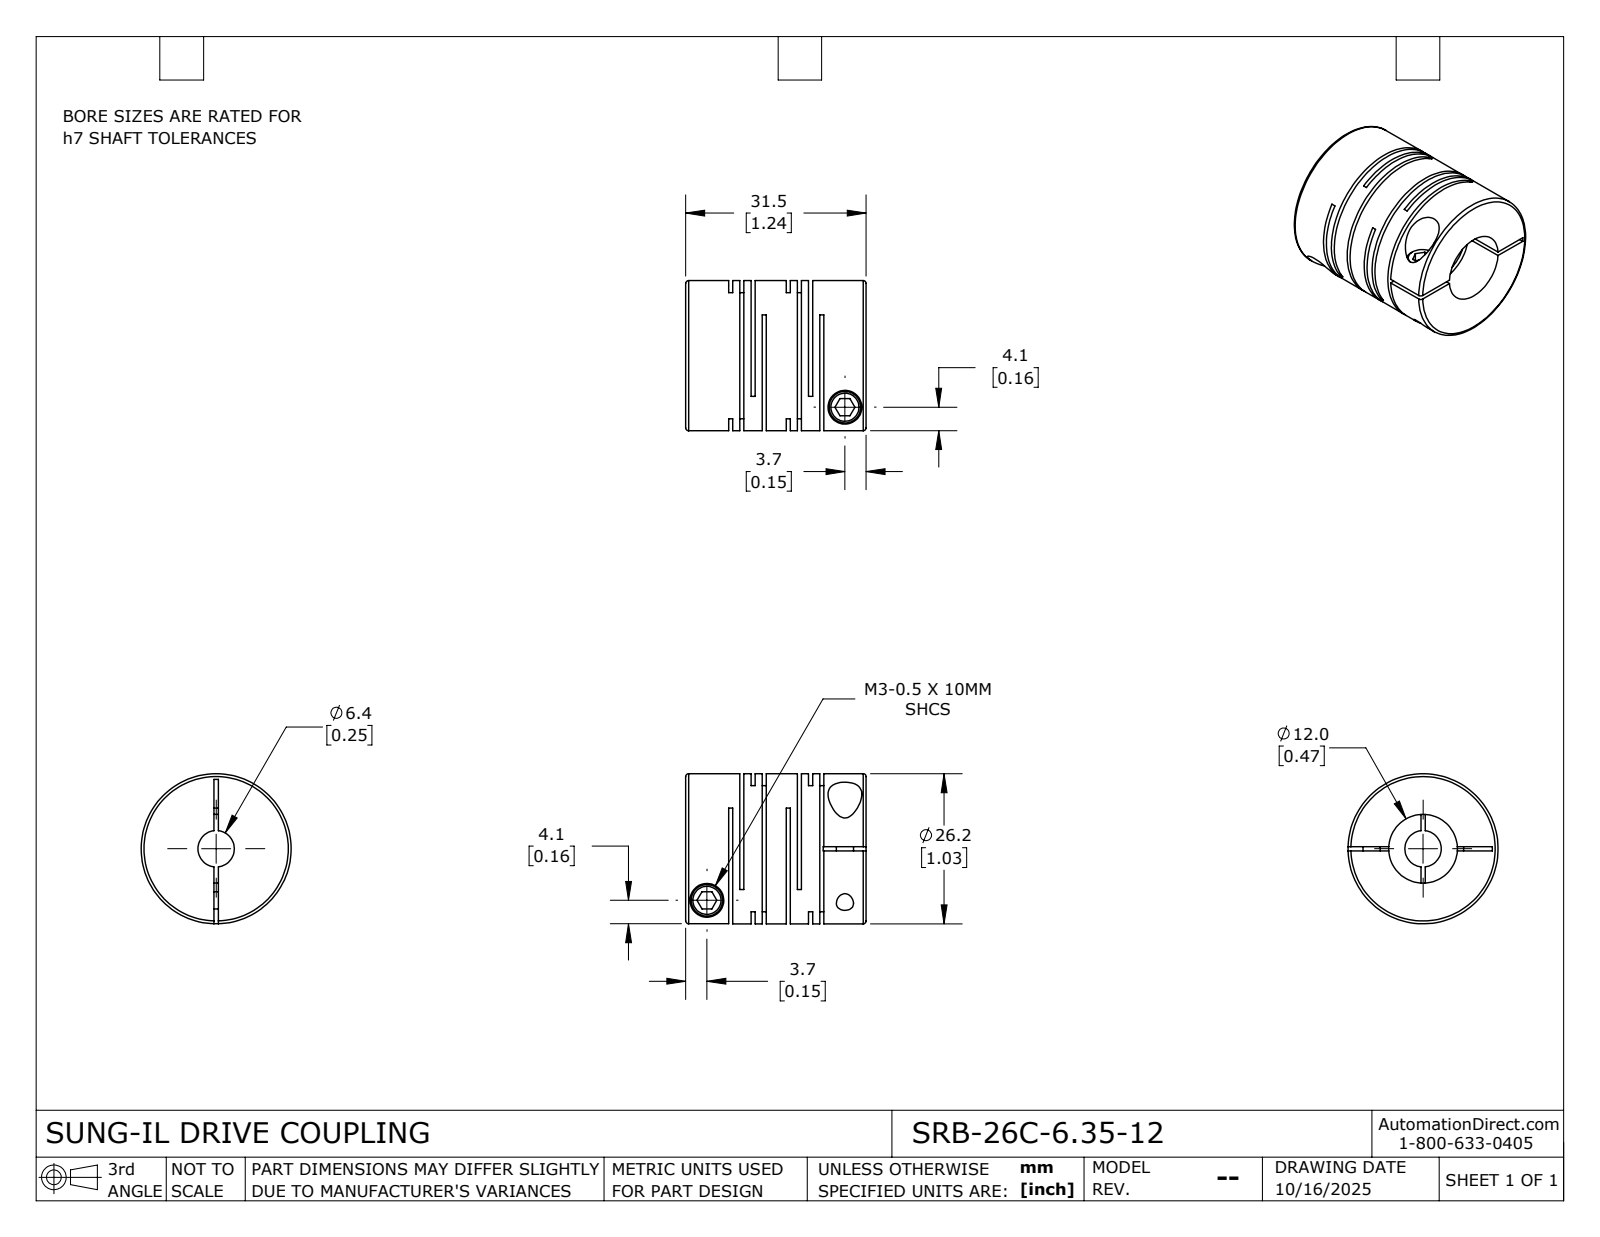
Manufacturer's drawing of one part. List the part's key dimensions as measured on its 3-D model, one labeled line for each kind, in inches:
Part name (STEP PRODUCT): SRB-26C-6.35-12
STEP written by: SolidWorks 2024 (CONFIG_CONTROL_DESIGN)
Units: inches
Bodies: 1 solid, 115 faces (60 planar, 42 cylindrical, 13 other)
Overall size (bounding box): 1.24 × 1.031 × 1.031
Volume: 0.711 in³ · Surface area: 15.99 in²
Round holes (diameter × count): ⌀0.118 ×2, ⌀0.232 ×2, ⌀0.25 ×1, ⌀0.472 ×1
Round bosses / shafts (diameter × count): ⌀0.217 ×2, ⌀1.031 ×1
Main face-to-face distances: 0.077, 0.396, 0.028, 0.154, 0.319, 0.472, 0.049, 0.105, 0.368, 0.549
